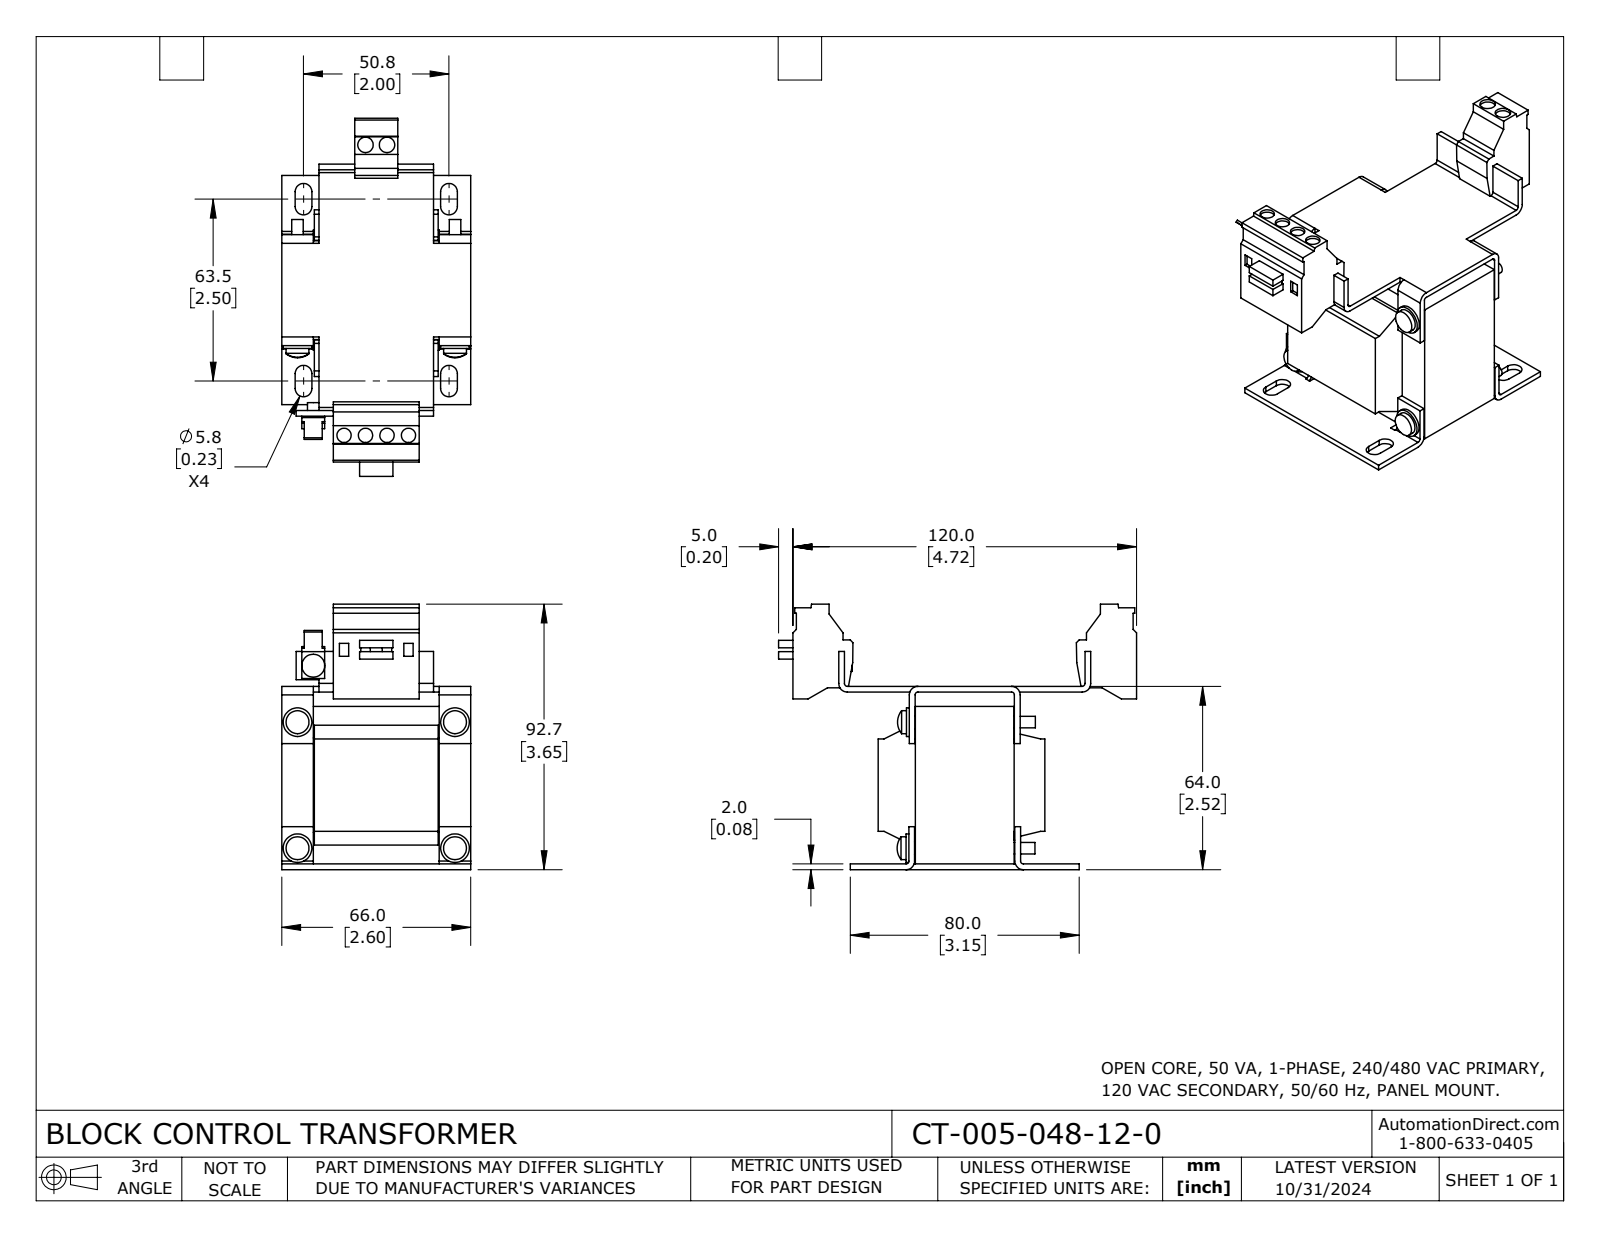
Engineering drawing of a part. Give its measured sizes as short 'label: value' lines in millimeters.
name: CT-005-048-12-0
written by: SolidWorks 2023 (CONFIG_CONTROL_DESIGN)
unit: mm
bodies: 1 solid, 325 faces (229 planar, 92 cylindrical, 4 other)
size: 125 × 92.7 × 66
volume: 207 000 mm³; area: 55 320 mm²
holes: 4× ⌀5, 2× ⌀5.4
bosses: 5× ⌀8, 5× ⌀4, 4× ⌀10, 4× ⌀4.5
rounds: 8× R2.9, 6× R1, 6× R3
face distances: 2, 62, 55, 11, 64, 11.4, 54.6, 60, 7, 44
hole spacings: 7.5, 101.7, 15, 101.4, 102.5, 22.5
